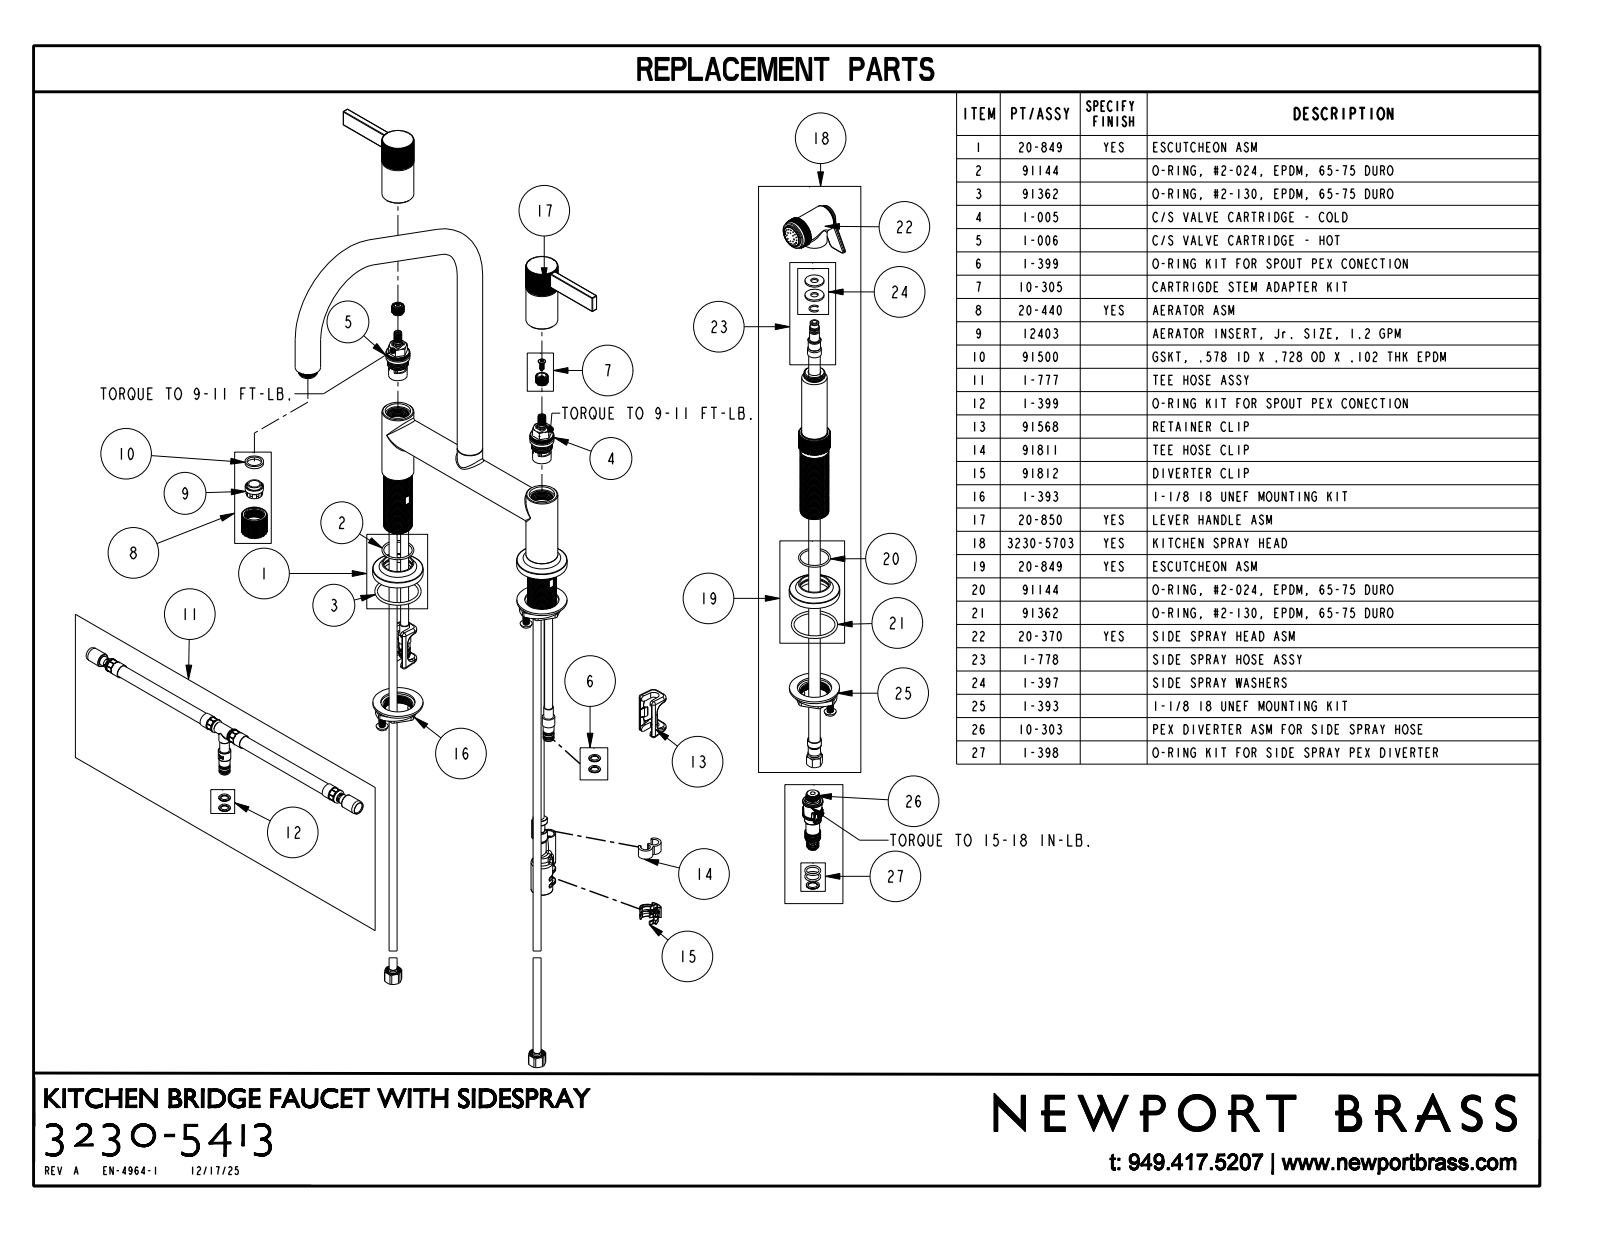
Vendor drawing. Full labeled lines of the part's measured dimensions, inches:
Part name (STEP PRODUCT): 3230-5413
STEP written by: CREO PARAMETRIC BY PTC INC, 2023134 (CONFIG_CONTROL_DESIGN)
Units: inches
Bodies: 6 solids, 1838 faces (1031 planar, 603 cylindrical, 204 other)
Overall size (bounding box): 17.915 × 16.439 × 10.89
Volume: 49.46 in³ · Surface area: 215.2 in²
Round holes (diameter × count): ⌀0.535 ×2, ⌀0.231 ×1, ⌀0.56 ×1, ⌀0.62 ×1, ⌀0.691 ×1, ⌀0.835 ×1, ⌀0.93 ×1, ⌀0.968 ×1, ⌀1.04 ×1
Round bosses / shafts (diameter × count): ⌀1 ×4, ⌀1.98 ×3, ⌀1.25 ×3, ⌀0.51 ×2, ⌀1.1 ×1, ⌀1.023 ×1, ⌀0.96 ×1, ⌀0.923 ×1
Partial cylindrical surfaces — rounded edges, fillets, slot ends (radius × count): R0.02 ×12, R0.04 ×10, R0.07 ×5, R0.03 ×4, R0.06 ×4, R0.16 ×2, R0.34 ×2, R0.332 ×1
Main face-to-face distances: 0.25, 6.048, 5.038, 1.01, 5.017, 0.021, 1.031, 0.899, 5.344, 5.994
Hole centre spacings: 4, 9.849, 8, 9
